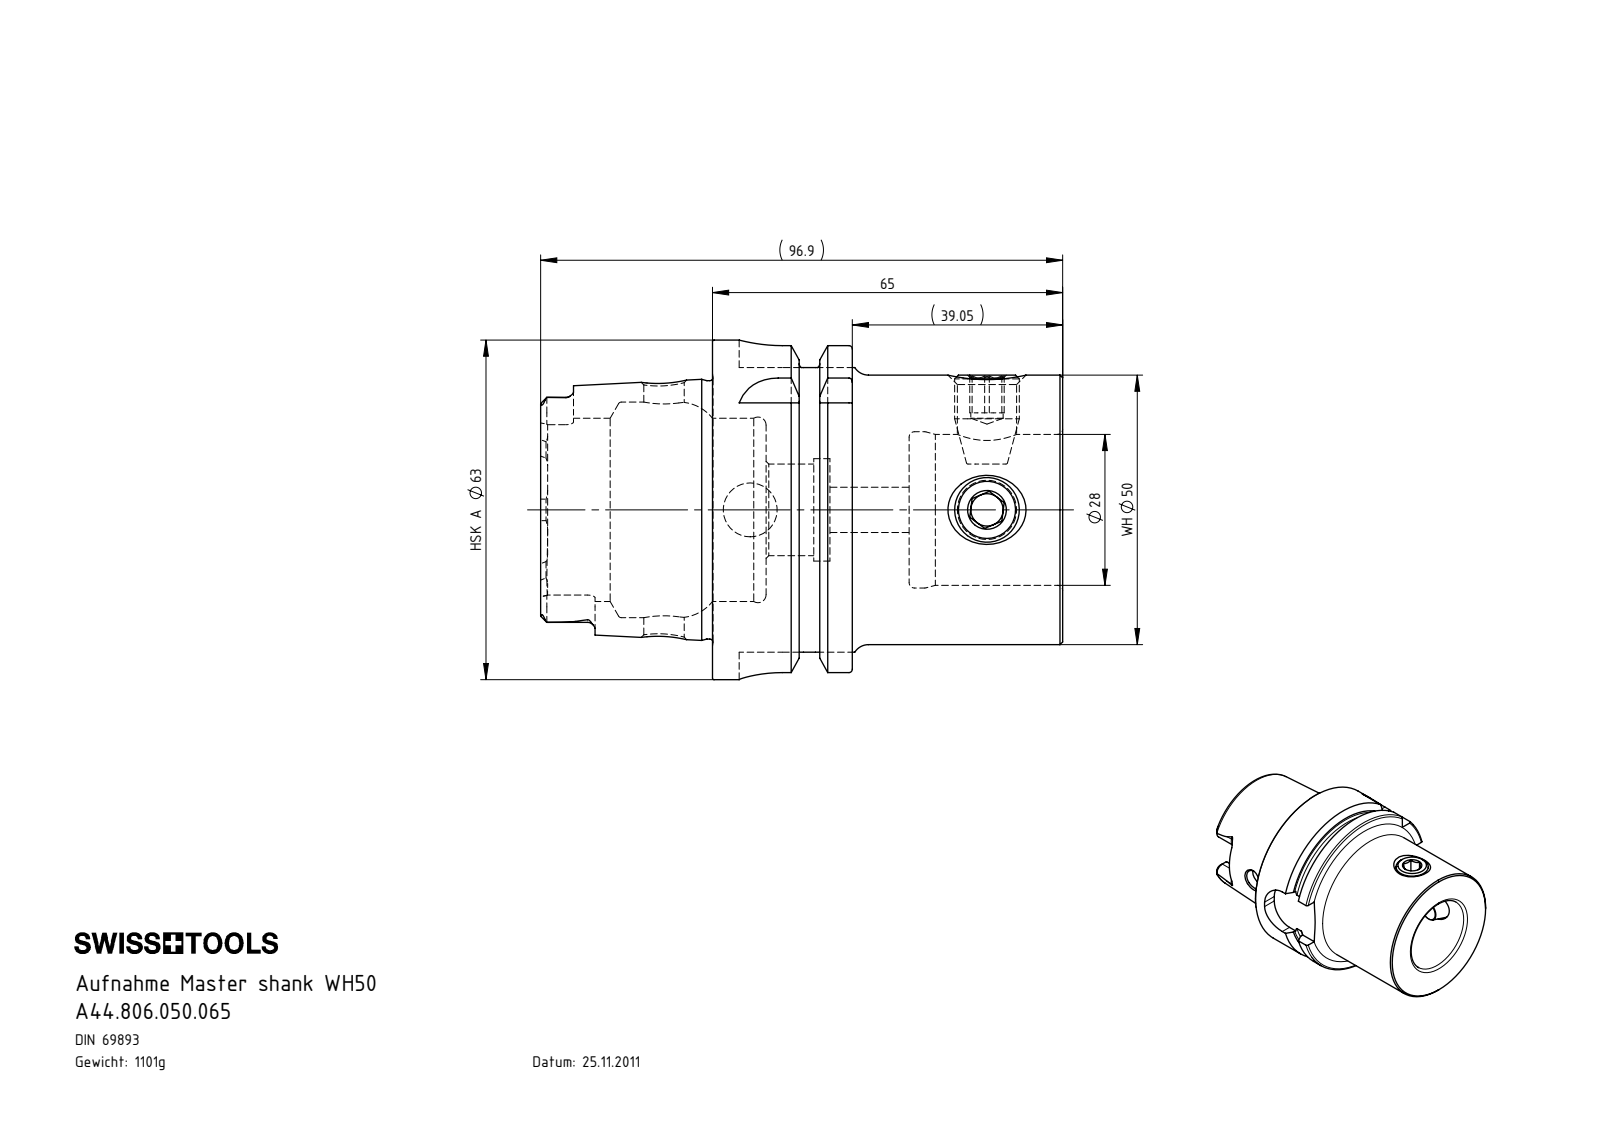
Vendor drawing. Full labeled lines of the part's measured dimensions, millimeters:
Part name (STEP PRODUCT): HA6.WH5.K01.065; HA6-WH5.K01.065_B; WH5-ER1.001.017
STEP written by: SolidWorks 2017 (AUTOMOTIVE_DESIGN)
Units: millimetres
Bodies: 3 solids, 184 faces (76 planar, 39 cylindrical, 69 other)
Overall size (bounding box): 96.9 × 63 × 63
Volume: 140 307 mm³ · Surface area: 32 965 mm²
Round holes (diameter × count): ⌀6 ×2, ⌀11 ×2, ⌀7.5 ×1, ⌀8.4 ×1, ⌀10 ×1, ⌀17 ×1, ⌀19 ×1, ⌀28 ×1, ⌀29 ×1, ⌀34 ×1, ⌀40 ×1
Round bosses / shafts (diameter × count): ⌀12 ×2, ⌀63 ×1, ⌀54.95 ×1, ⌀50 ×1, ⌀47.94 ×1
Partial cylindrical surfaces — rounded edges, fillets, slot ends (radius × count): R1.4 ×6, R2.88 ×4, R8 ×4
Main face-to-face distances: 65, 9.95, 55.05, 36.5, 26.55, 28.5, 16, 25.95, 10.55, 39.05
Hole centre spacings: 43.95, 59.95
